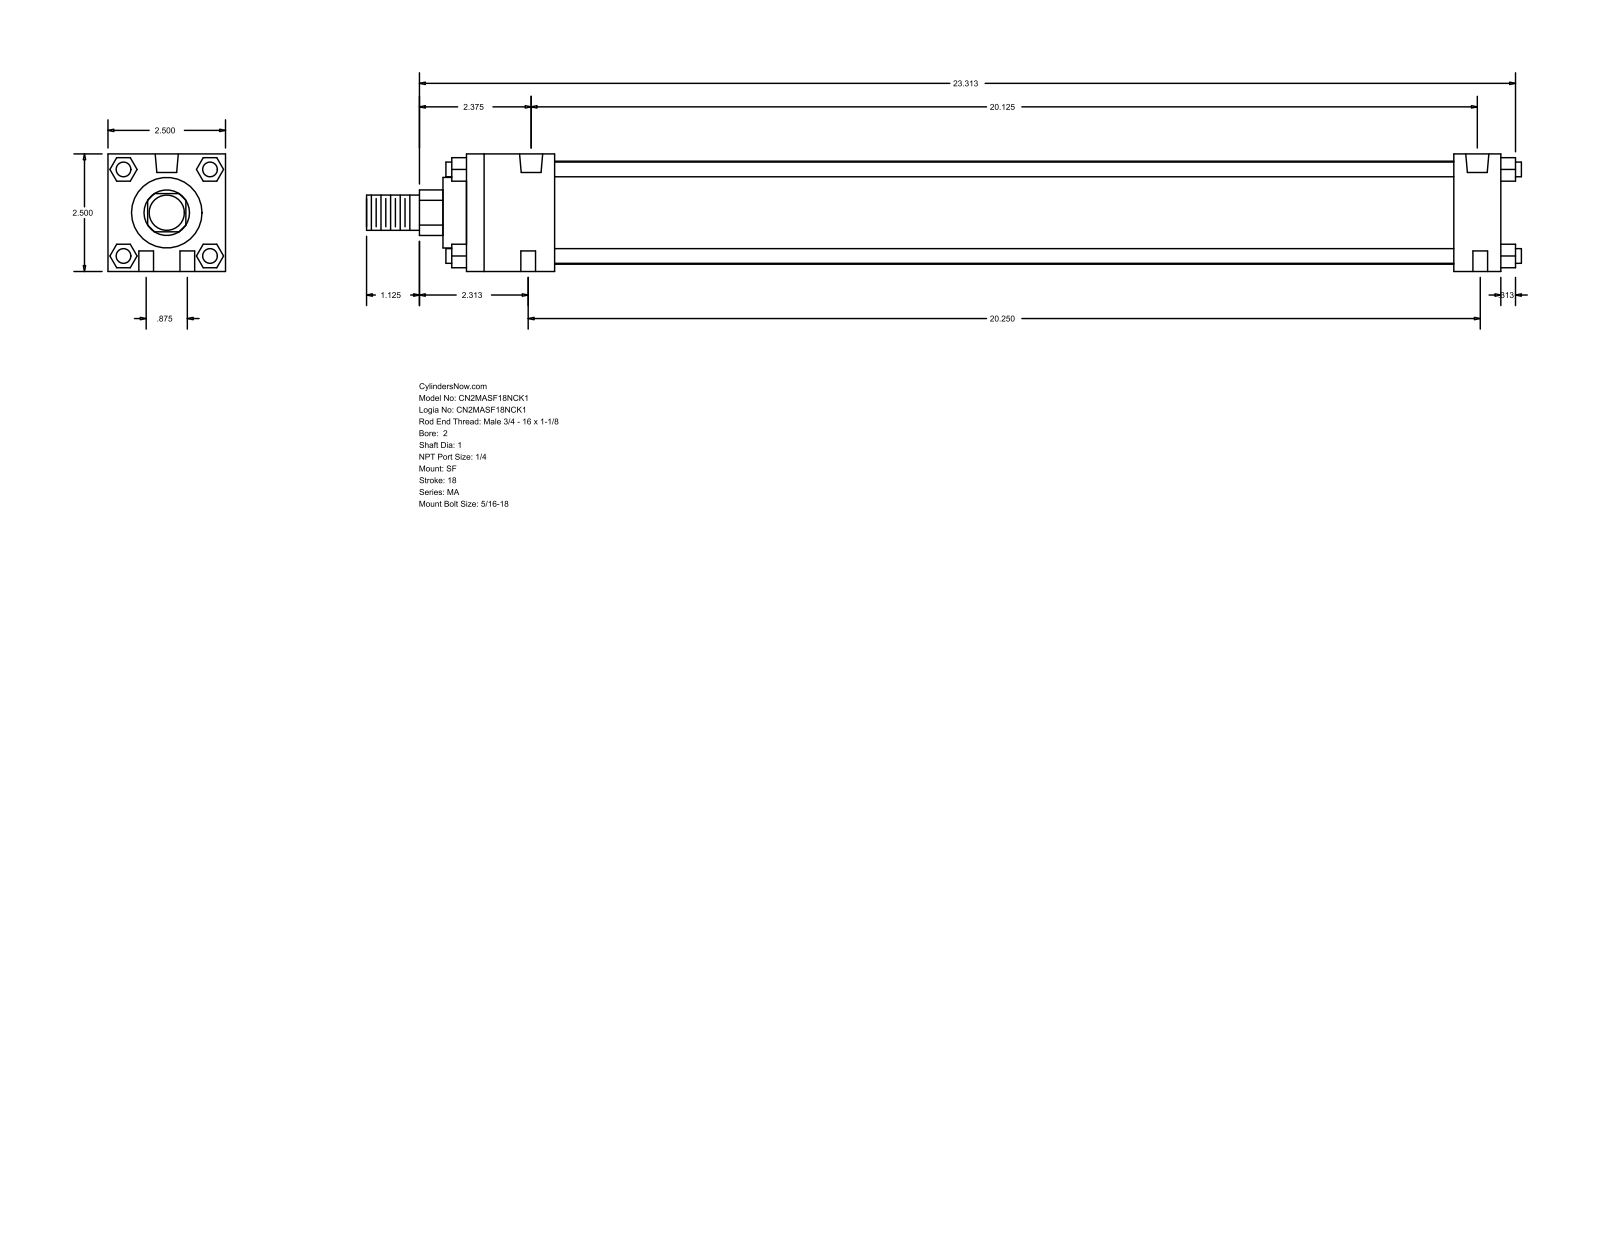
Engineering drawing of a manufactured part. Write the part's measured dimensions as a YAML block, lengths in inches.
part_name: "MA_SF__0200_1"
step_written_by: "GSSL Pune (CONFIG_CONTROL_DESIGN)"
units: inches
bodies: {solids: 0, faces: 124, planar: 94, cylindrical: 30, other: 0}
overall_size: [24.563, 2.5, 2.5]
round_holes:
  - {diameter: 0.313, count: 6}
  - {diameter: 0.492, count: 2}
round_bosses_or_shafts:
  - {diameter: 0.313, count: 4}
  - {diameter: 2.19, count: 1}
  - {diameter: 1.5, count: 1}
  - {diameter: 1, count: 1}
  - {diameter: 0.75, count: 1}
partial_cylinders:
  - {radius: 0.484, count: 1}
face_to_face_distances: [2.5, 22, 0.5, 1, 21, 1.875, 19.125, 20.125, 0.92, 1.593]
hole_center_spacings: [0.442, 20.192, 0.875, 20.125, 20.25, 20.269]
